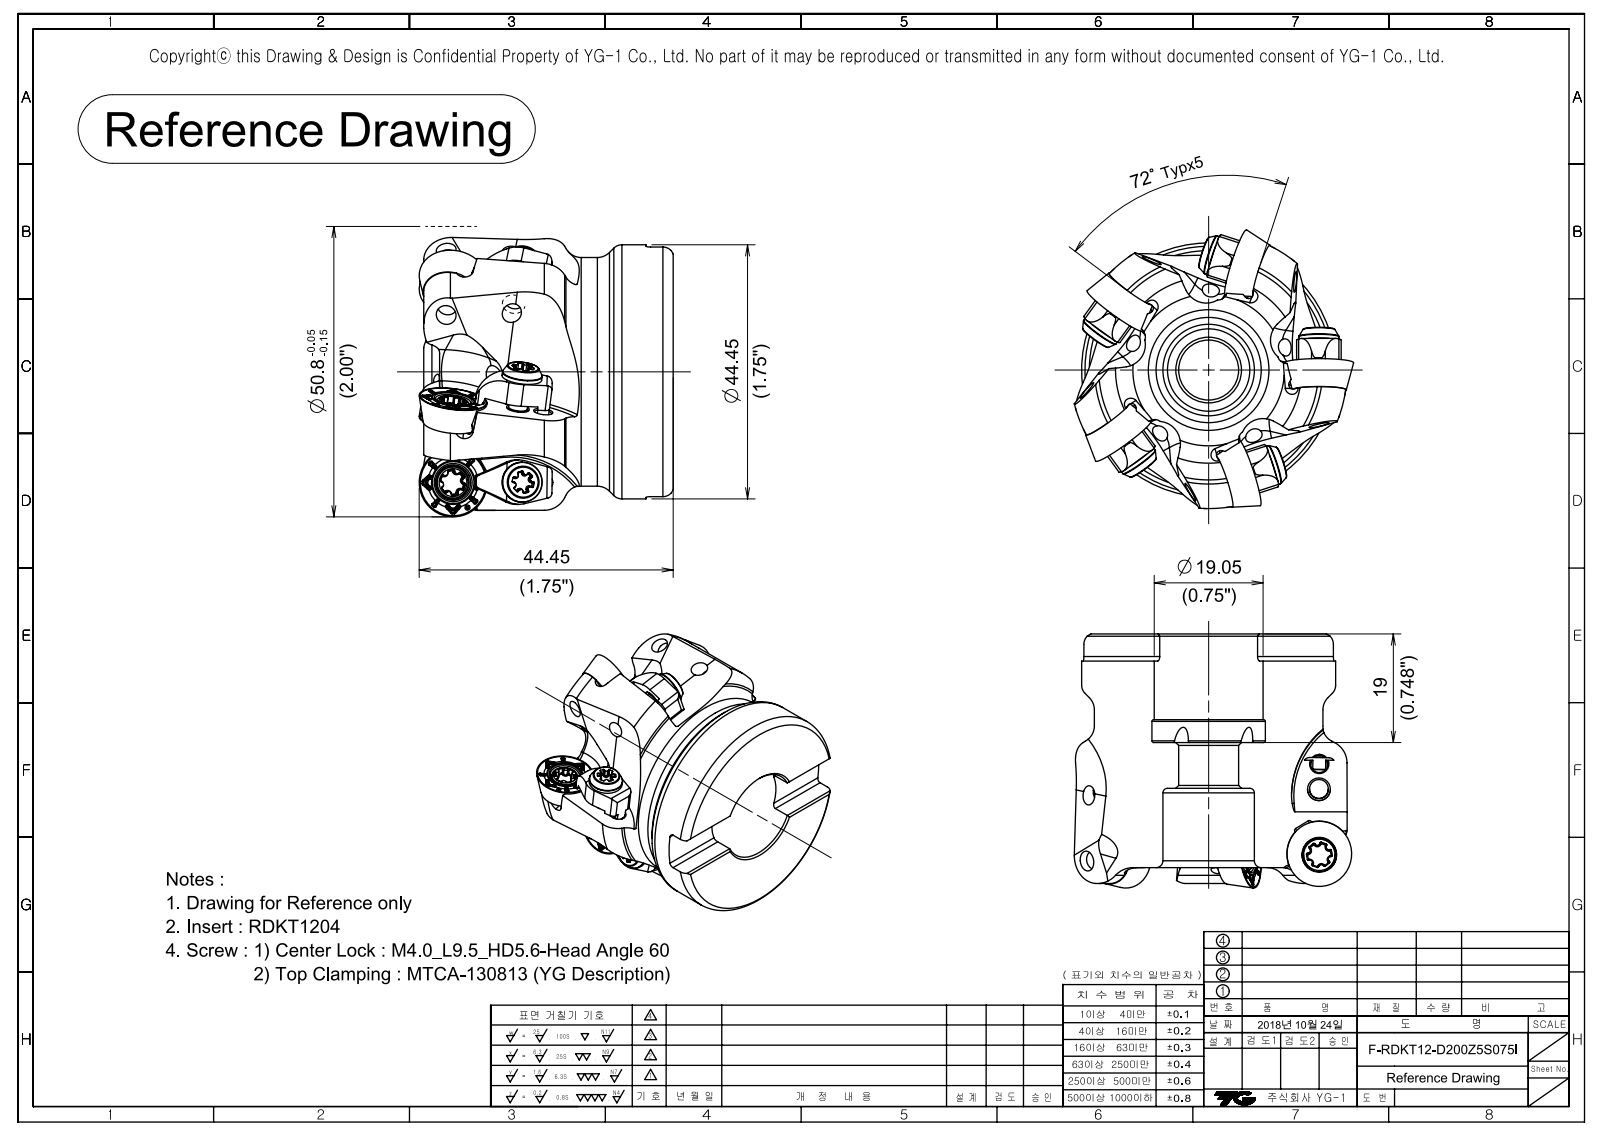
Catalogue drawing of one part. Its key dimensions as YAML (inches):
part_name: "CUTTER_F-RDKT12-D200Z5S075I"
step_written_by: "SIEMENS PLM Software NX 10.0 (CONFIG_CONTROL_DESIGN)"
units: inches
bodies: {solids: 21, faces: 3198, planar: 386, cylindrical: 385, other: 2427}
overall_size: [1.924, 1.92, 1.75]
volume: 2.726
surface_area: 29.18
round_holes:
  - {diameter: 0.118, count: 10}
  - {diameter: 0.13, count: 5}
  - {diameter: 0.138, count: 5}
  - {diameter: 0.173, count: 5}
  - {diameter: 0.177, count: 5}
  - {diameter: 0.413, count: 1}
  - {diameter: 0.63, count: 1}
  - {diameter: 0.75, count: 1}
  - {diameter: 0.781, count: 1}
round_bosses_or_shafts:
  - {diameter: 0.157, count: 10}
  - {diameter: 0.276, count: 5}
  - {diameter: 0.217, count: 5}
  - {diameter: 0.169, count: 5}
  - {diameter: 0.13, count: 2}
  - {diameter: 1.75, count: 1}
  - {diameter: 1.575, count: 1}
partial_cylinders:
  - {radius: 0.006, count: 120}
  - {radius: 0.012, count: 30}
  - {radius: 0.018, count: 30}
  - {radius: 0.059, count: 30}
  - {radius: 0.016, count: 15}
  - {radius: 0.039, count: 15}
  - {radius: 0.02, count: 10}
  - {radius: 0.03, count: 10}
face_to_face_distances: [0.173, 0.224, 0.157, 1.609, 0.067, 0.398, 0.24, 1.422, 0.187, 0.861]
hole_center_spacings: [0.176, 0.451, 0.622, 0.627, 0.446, 0.446, 0.45]
